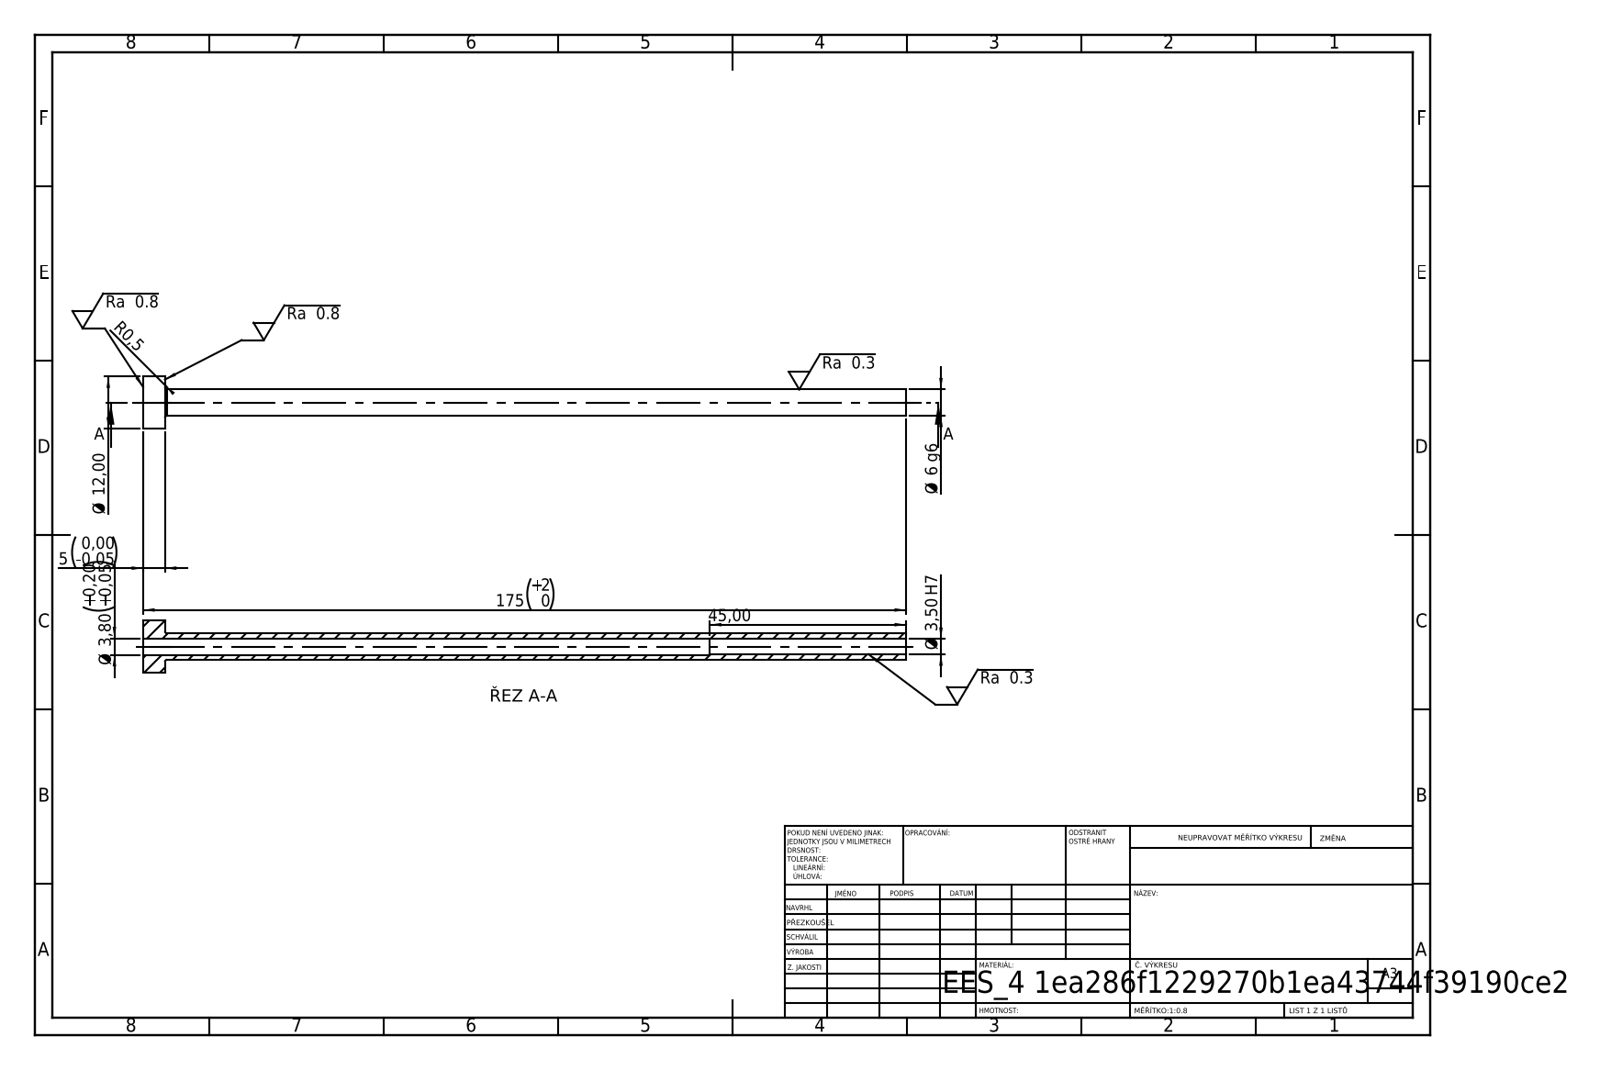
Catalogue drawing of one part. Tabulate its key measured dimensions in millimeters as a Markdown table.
| quantity | value |
| --- | --- |
| STEP written by | SolidWorks 2019 (CONFIG_CONTROL_DESIGN) |
| units | millimeters |
| bodies | 1 solid, 14 faces (4 planar, 8 cylindrical, 2 other) |
| overall size | 175 × 12 × 12 |
| volume | 3 466 mm³ |
| surface area | 5 643 mm² |
| round holes (diameter × count) | 3.5 × 1, 3.8 × 1 |
| round bosses / shafts (diameter × count) | 12 × 1, 6 × 1 |
| main face-to-face distances | 5, 175, 170, 130, 125, 45 |
